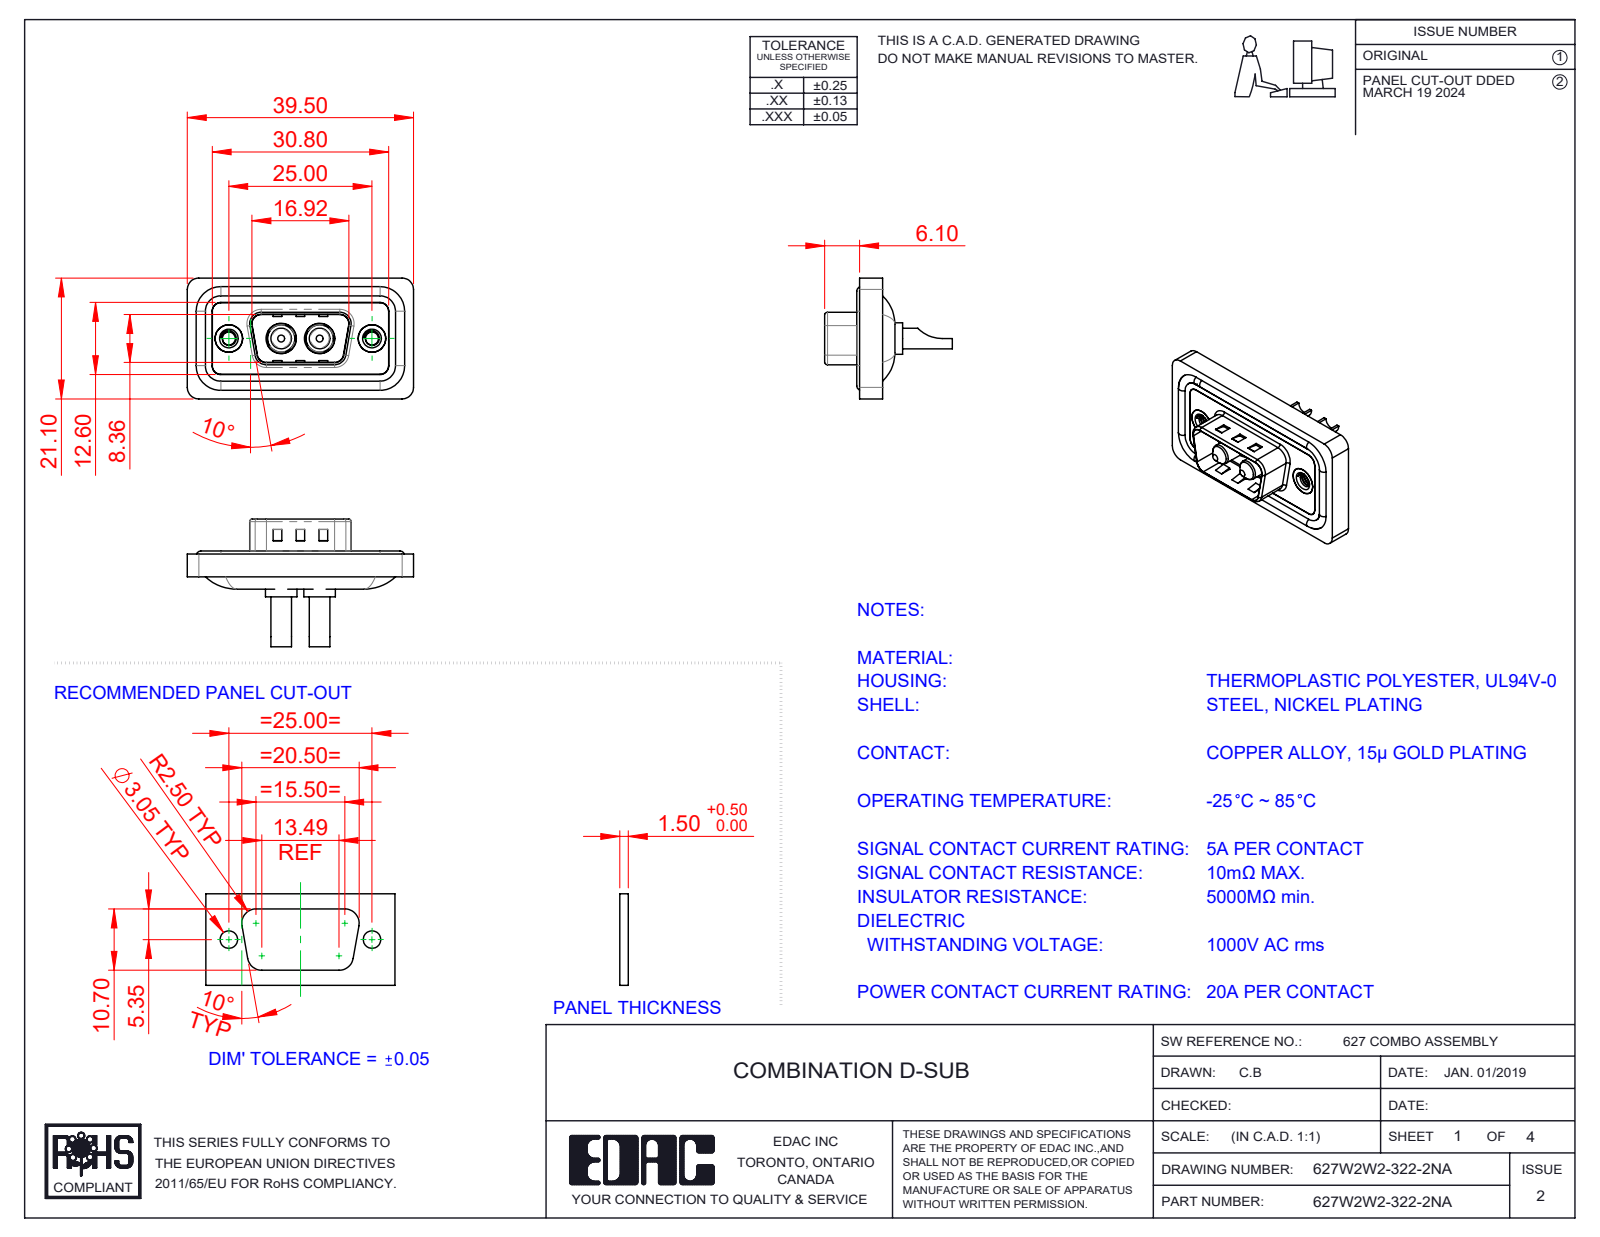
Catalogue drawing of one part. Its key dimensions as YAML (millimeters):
part_name: "627Combo Housing_2W2; 627Combo Shell Rear_09 Contacts; 627Combo Threaded Rivet_A; Power Pin_20A SC (+3 more)"
step_written_by: "SolidWorks 2023 (CONFIG_CONTROL_DESIGN)"
units: millimeters
bodies: {solids: 11, faces: 501, planar: 171, cylindrical: 226, other: 104}
overall_size: [39.5, 22.3, 21.1]
volume: 4488
surface_area: 7146
round_holes:
  - {diameter: 2.26, count: 2}
  - {diameter: 2.7, count: 2}
  - {diameter: 4, count: 2}
  - {diameter: 4.8, count: 2}
  - {diameter: 4.85, count: 2}
  - {diameter: 5, count: 2}
  - {diameter: 5.3, count: 2}
round_bosses_or_shafts:
  - {diameter: 1.6, count: 4}
  - {diameter: 5.5, count: 2}
  - {diameter: 5.2, count: 2}
  - {diameter: 4.9, count: 2}
  - {diameter: 4.75, count: 2}
  - {diameter: 3.75, count: 2}
  - {diameter: 3.6, count: 2}
partial_cylinders:
  - {radius: 1.5, count: 22}
  - {radius: 2, count: 18}
  - {radius: 0.5, count: 8}
  - {radius: 1.6, count: 8}
  - {radius: 0.25, count: 4}
  - {radius: 0.6, count: 4}
  - {radius: 0.65, count: 4}
  - {radius: 0.9, count: 4}
face_to_face_distances: [0.4, 1.1, 2.9, 3.1, 0.5, 1.6, 1.5, 4, 2.5, 0.7]
hole_center_spacings: [9.14, 15.86, 6.72, 25]
